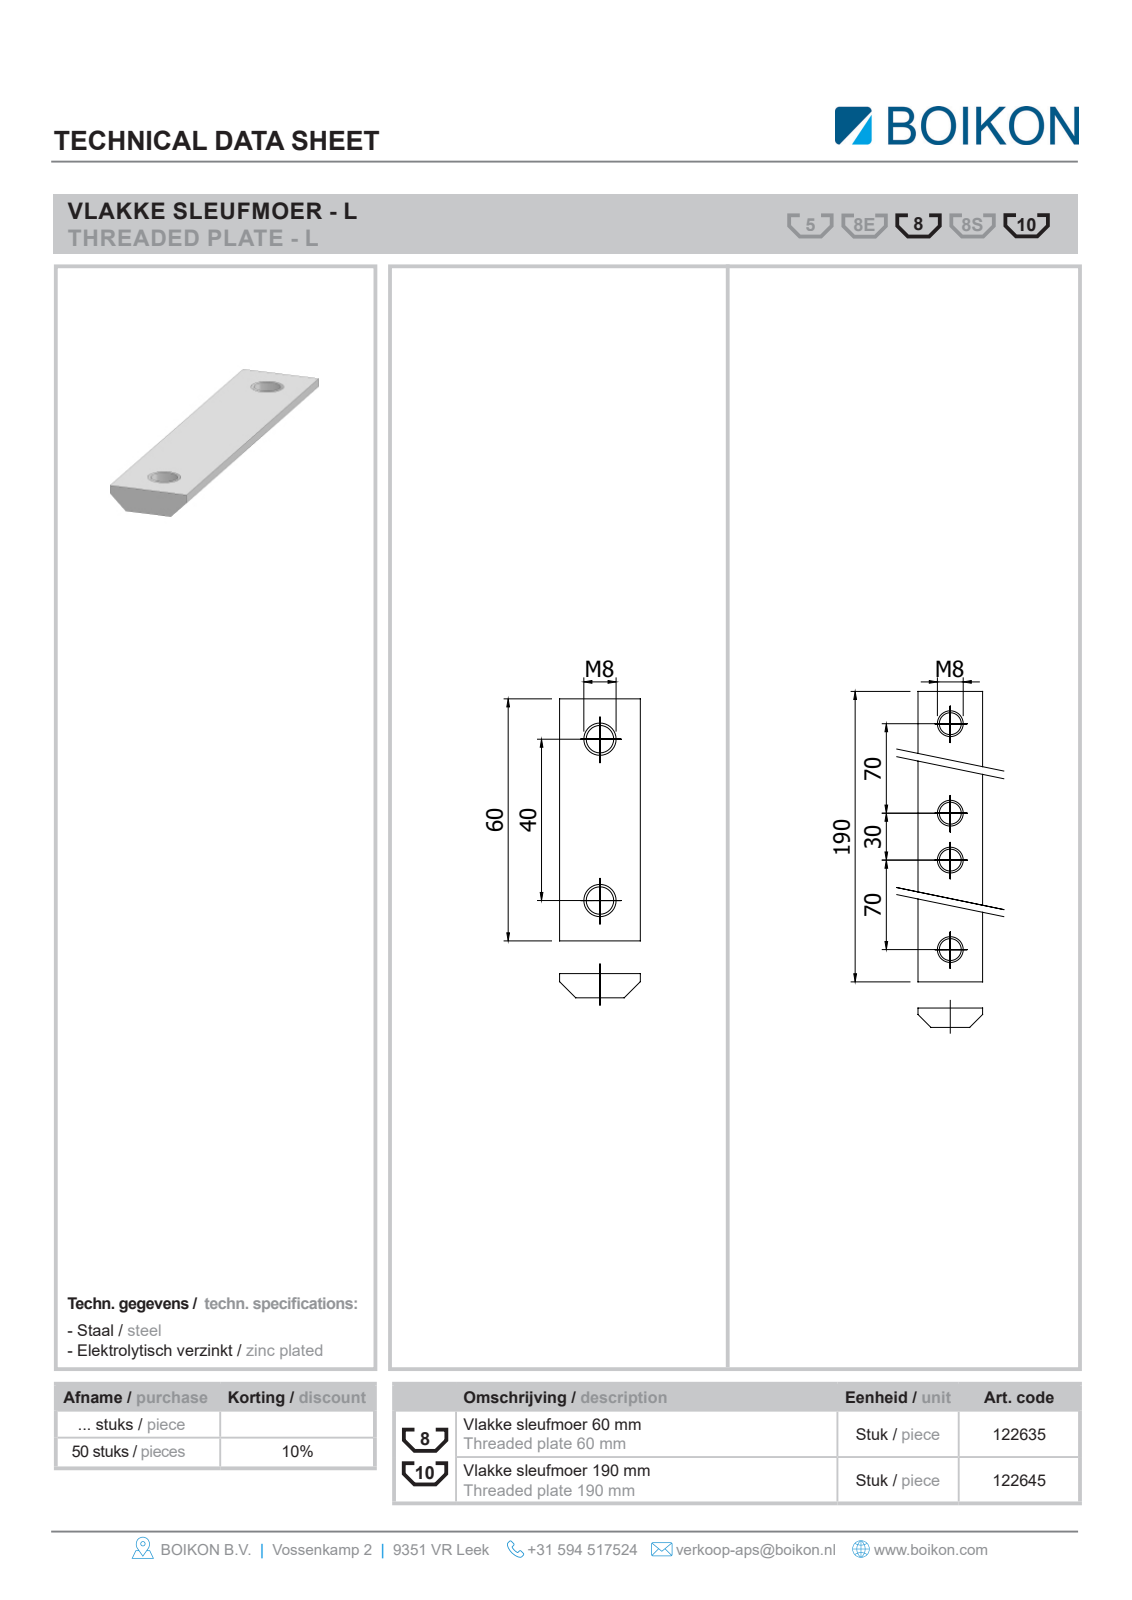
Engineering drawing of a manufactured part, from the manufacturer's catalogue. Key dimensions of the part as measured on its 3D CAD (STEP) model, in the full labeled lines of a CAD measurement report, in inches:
Part name (STEP PRODUCT): Root; 122645Sleufmoer vlak 8 en 10 - 4x M8 L=190BOIKON
STEP written by: HiCAD 2013 1802.4 Build 509 (AUTOMOTIVE_DESIGN)
Units: inches
Bodies: 1 solid, 12 faces (8 planar, 4 cylindrical, 0 other)
Overall size (bounding box): 7.48 × 0.768 × 0.472
Volume: 1.097 in³ · Surface area: 14.26 in²
Round holes (diameter × count): ⌀0.315 ×4
Main face-to-face distances: 0.236, 0.768, 7.48
Hole centre spacings: 2.756, 3.937, 1.181, 6.693
